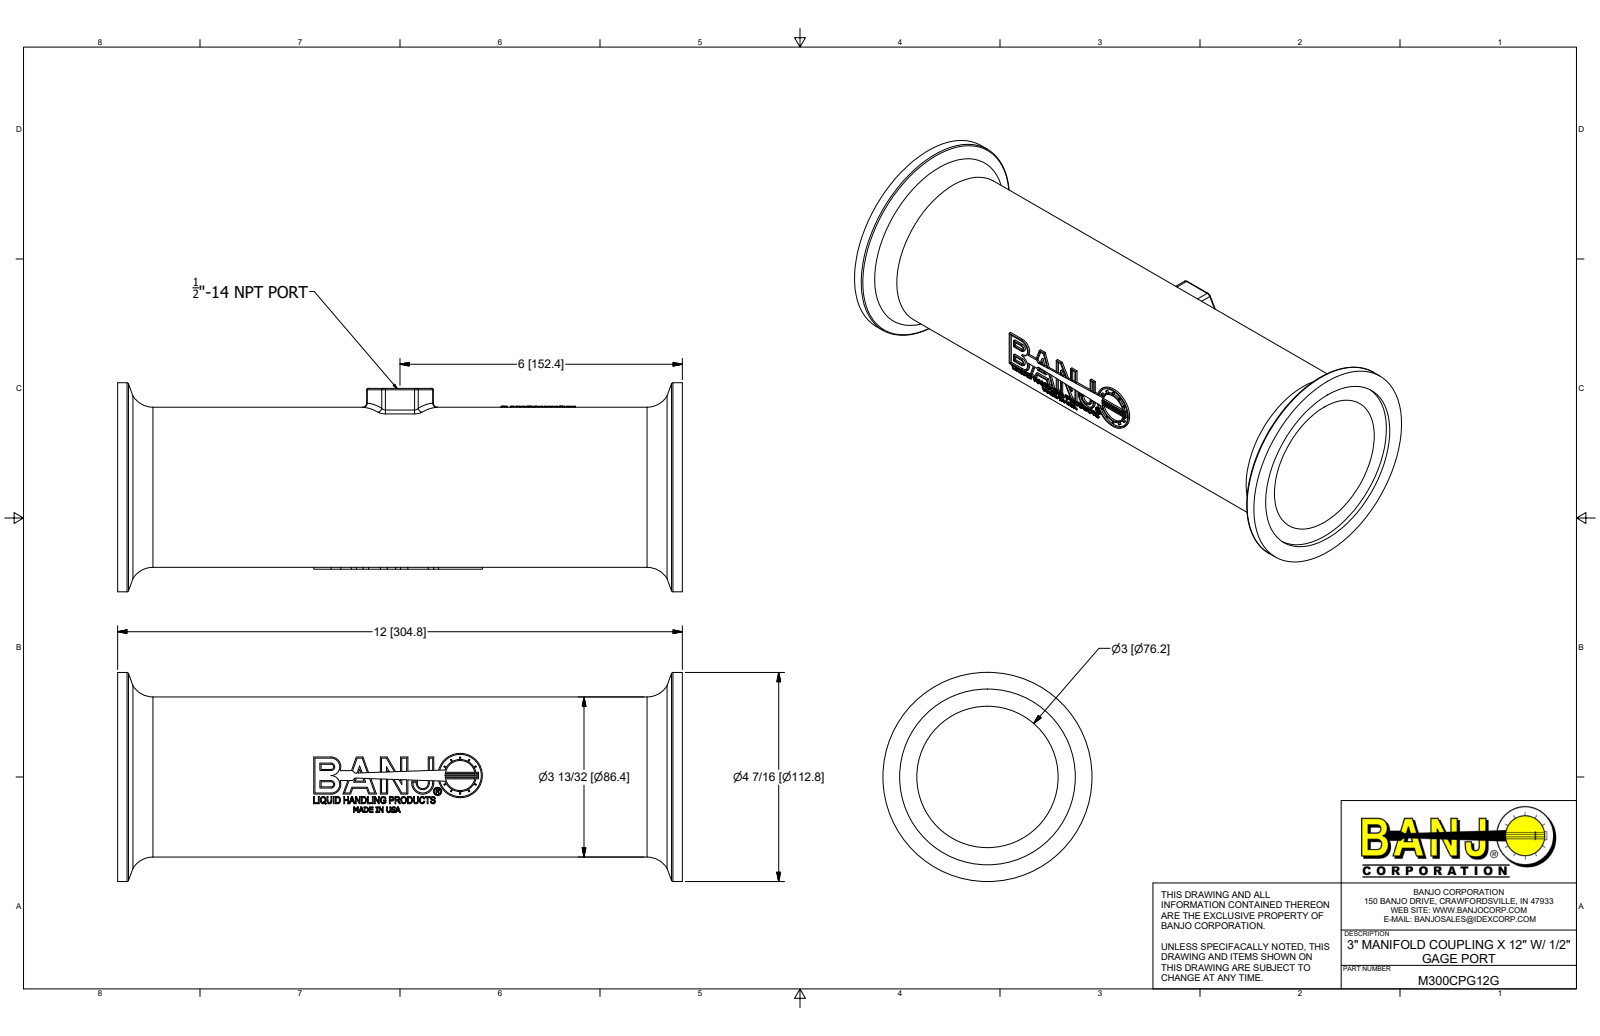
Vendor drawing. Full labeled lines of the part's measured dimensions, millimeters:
Part name (STEP PRODUCT): M300CPG12G; M300CPG12GX
STEP written by: Autodesk Inventor 2017 (AUTOMOTIVE_DESIGN)
Units: millimetres
Bodies: 4 solids, 830 faces (415 planar, 114 cylindrical, 301 other)
Overall size (bounding box): 304.8 × 112.78 × 112.78
Volume: 461 727 mm³ · Surface area: 176 967 mm²
Round holes (diameter × count): ⌀16.14 ×1, ⌀17.48 ×1, ⌀22.8 ×1, ⌀76.2 ×1, ⌀94.74 ×1
Round bosses / shafts (diameter × count): ⌀112.78 ×1, ⌀86.36 ×1, ⌀24 ×1
Partial cylindrical surfaces — rounded edges, fillets, slot ends (radius × count): R2.29 ×8, R0.76 ×6, R1.4 ×2, R2 ×2, R4.7 ×2, R5.3 ×2, R2.93 ×1, R3.53 ×1
Main face-to-face distances: 2.54, 302.26, 304.8, 299.72, 1.02, 96.52, 97.54, 0.6, 31.74, 31.76
Hole centre spacings: 32.46
